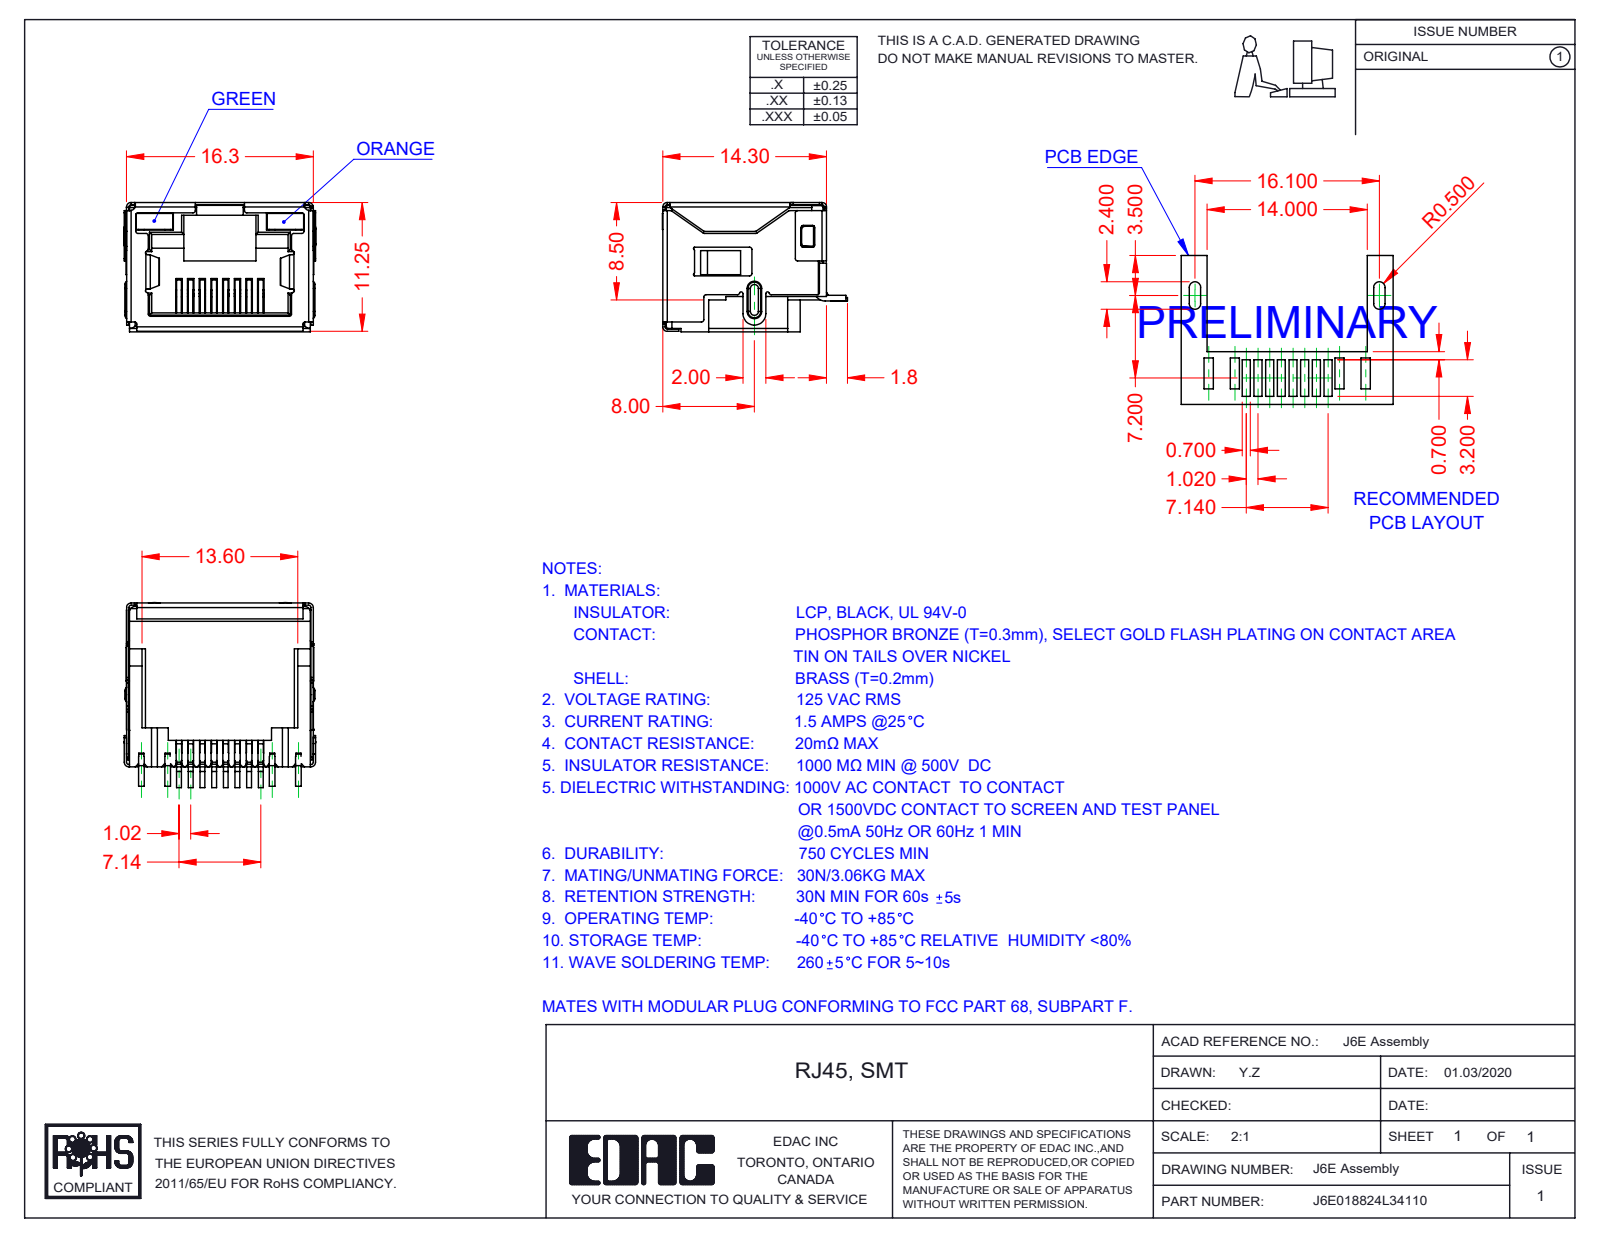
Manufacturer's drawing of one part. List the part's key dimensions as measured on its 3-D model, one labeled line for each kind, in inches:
Part name (STEP PRODUCT): J6E018824L34110; 6E Shield_LED; 6E Contacts; 6E Insulator_LED (+2 more)
STEP written by: SolidWorks 2016 (CONFIG_CONTROL_DESIGN)
Units: inches
Bodies: 12 solids, 1496 faces (1099 planar, 347 cylindrical, 50 other)
Overall size (bounding box): 0.659 × 0.636 × 0.445
Volume: 0.068 in³ · Surface area: 6.27 in²
Partial cylindrical surfaces — rounded edges, fillets, slot ends (radius × count): R0.008 ×82, R0.01 ×17, R0.016 ×13, R0.02 ×13, R0.004 ×10, R0.006 ×7, R0.012 ×4, R0.039 ×3
Main face-to-face distances: 0.435, 0.632, 0.634, 0.624, 0.437, 0.445, 0.094, 0.028, 0.388, 0.019
